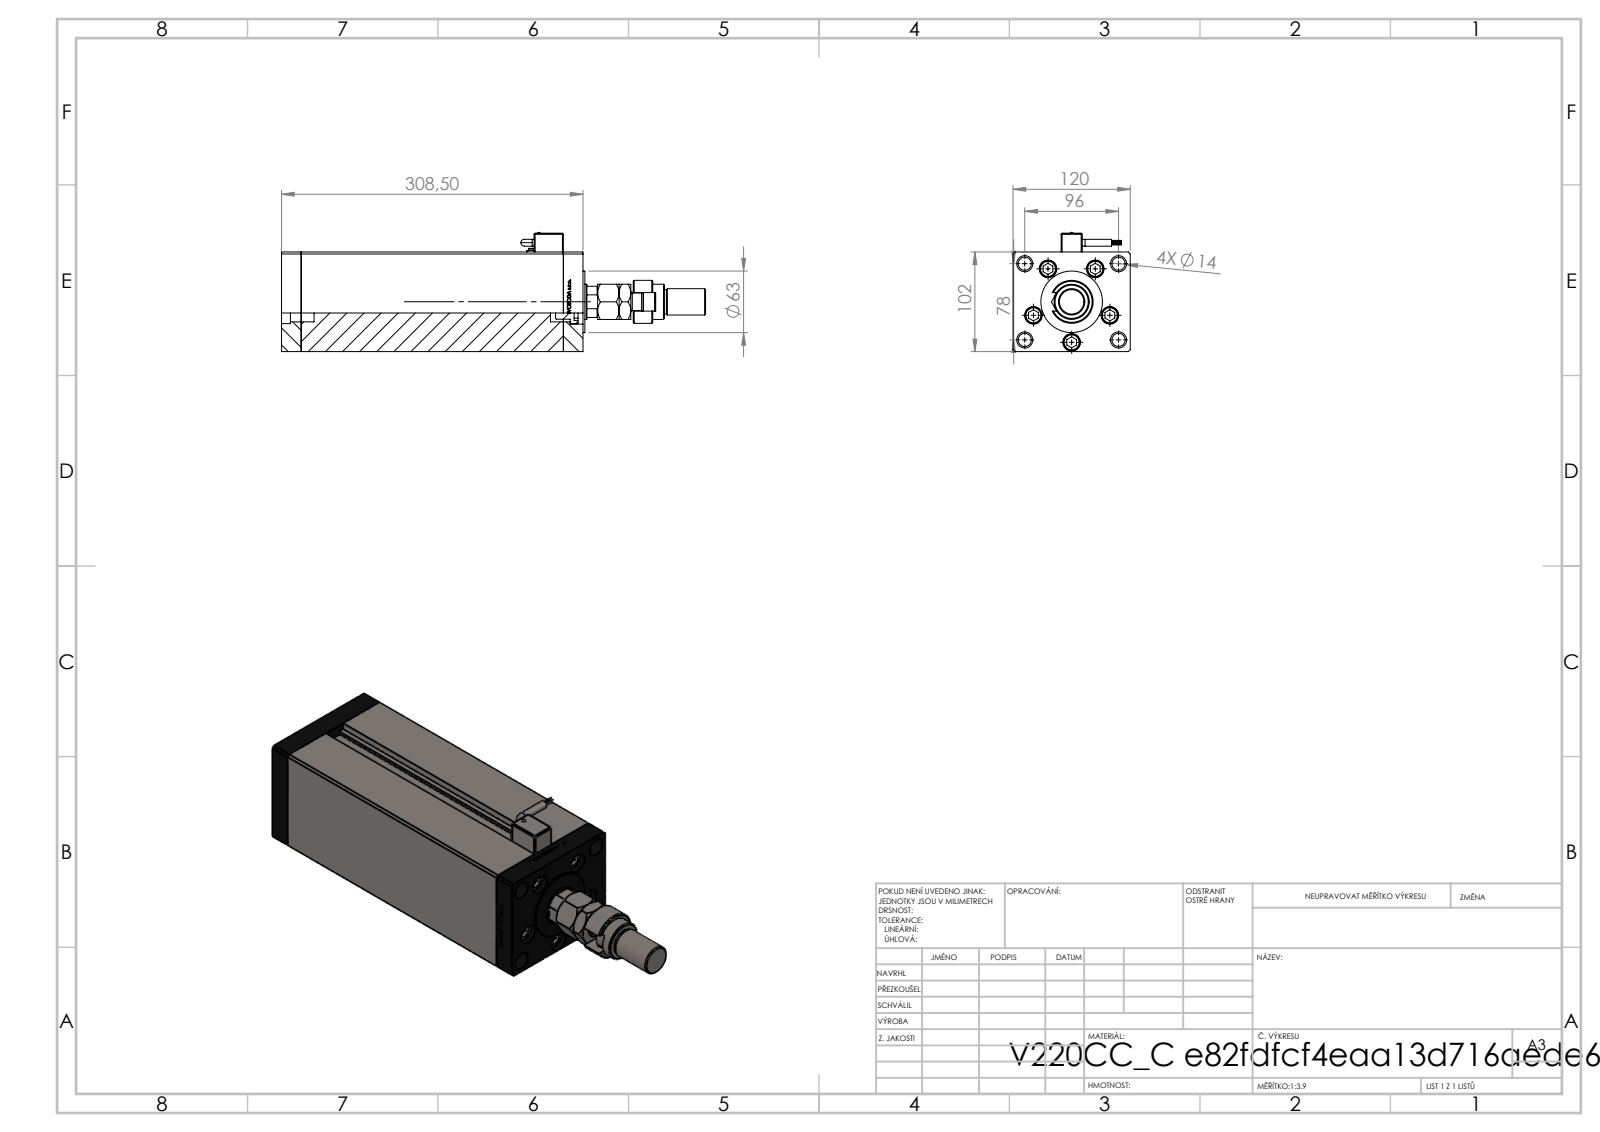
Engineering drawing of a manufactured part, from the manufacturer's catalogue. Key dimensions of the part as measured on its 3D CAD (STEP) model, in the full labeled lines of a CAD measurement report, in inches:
Part name (STEP PRODUCT): MFA; Magnetic_Switch_MSU4; V220C_VC_C; V220C FRONT (+4 more)
STEP written by: SolidWorks 2019 (CONFIG_CONTROL_DESIGN)
Units: inches
Bodies: 16 solids, 1352 faces (609 planar, 219 cylindrical, 524 other)
Overall size (bounding box): 17.087 × 4.807 × 4.724
Volume: 198.5 in³ · Surface area: 624.2 in²
Round holes (diameter × count): ⌀0.531 ×9, ⌀0.709 ×5, ⌀0.472 ×4, ⌀0.65 ×4, ⌀0.142 ×1, ⌀0.197 ×1, ⌀0.276 ×1, ⌀0.669 ×1, ⌀1.004 ×1
Round bosses / shafts (diameter × count): ⌀0.315 ×5, ⌀0.669 ×4, ⌀0.033 ×4, ⌀0.276 ×2, ⌀2.48 ×1, ⌀1.732 ×1, ⌀1.417 ×1, ⌀1.102 ×1
Partial cylindrical surfaces — rounded edges, fillets, slot ends (radius × count): R0.039 ×14, R0.037 ×2, R0.157 ×2, R0.374 ×1, R0.591 ×1, R0.689 ×1
Main face-to-face distances: 4.724, 4.016, 0.787, 10.571, 11.358, 1.348, 12.146, 10.797, 10.01, 0.561
Hole centre spacings: 1.634, 2.435, 0.96, 1.051, 1.887, 1.893, 1.962, 2.109
